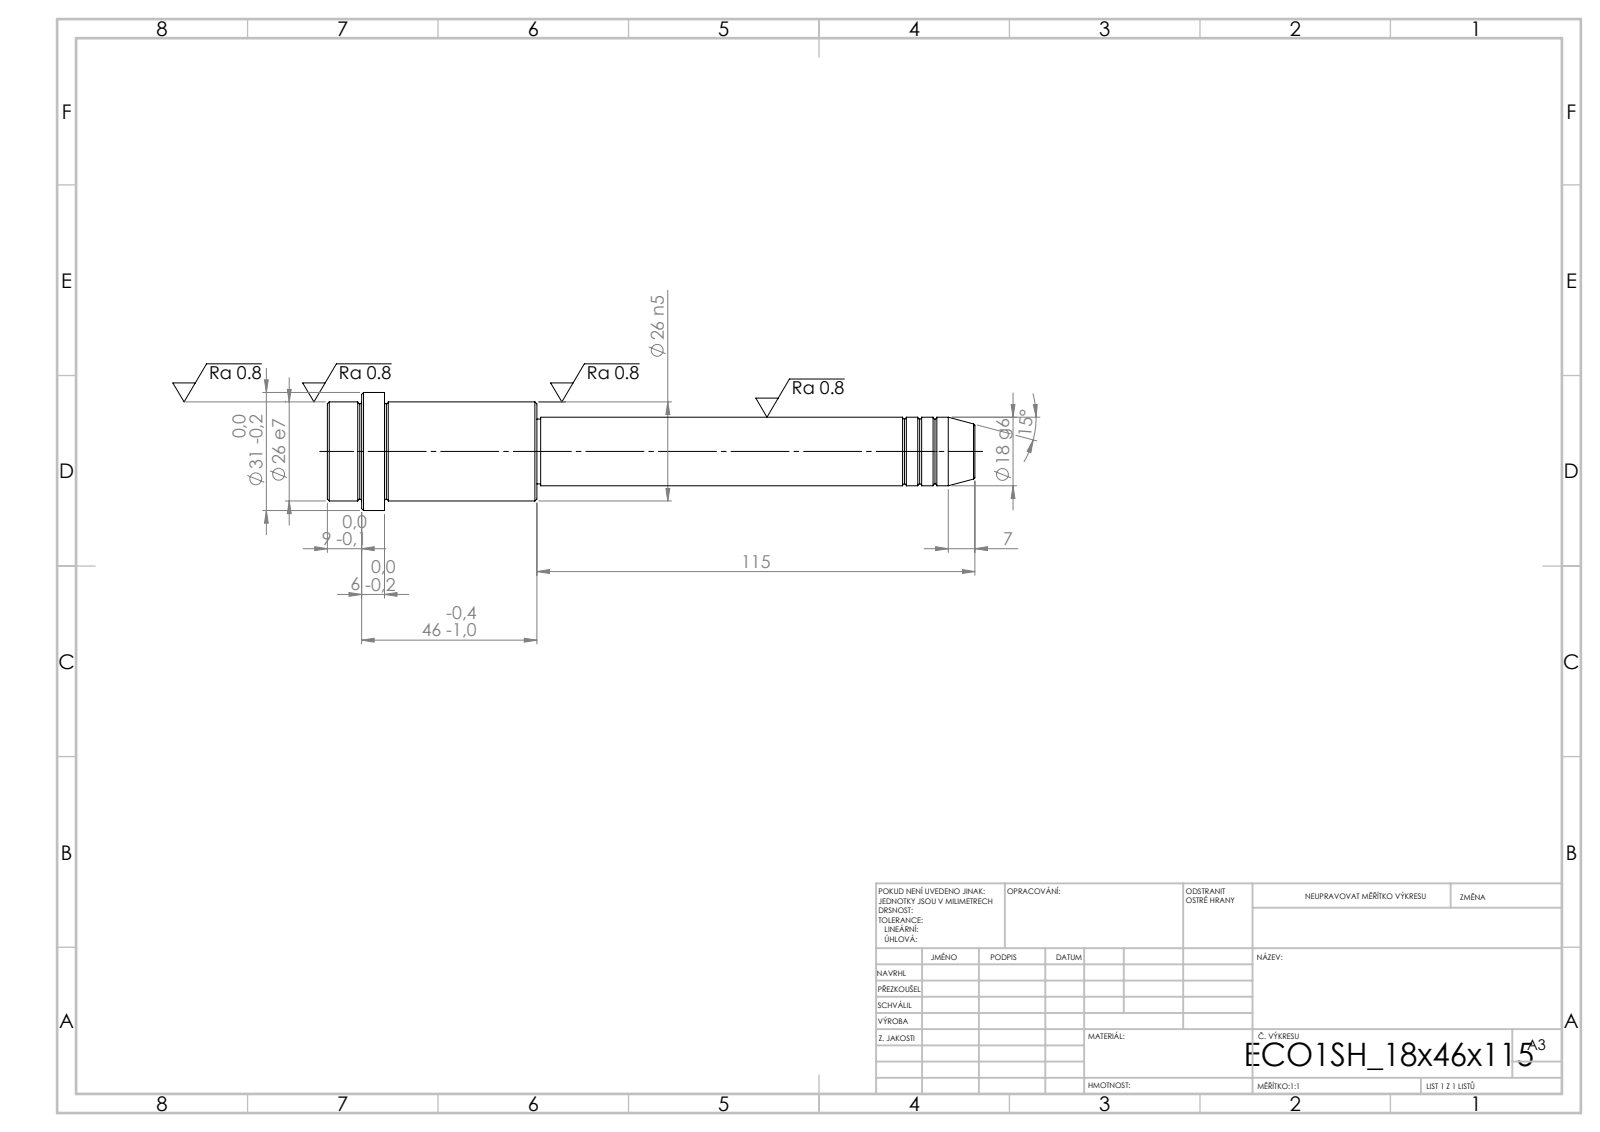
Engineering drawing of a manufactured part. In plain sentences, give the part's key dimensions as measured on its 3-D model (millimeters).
Its 3-D file was written by "SolidWorks 2019 (CONFIG_CONTROL_DESIGN)". It is 1 solid with 52 faces: 6 planar, 16 cylindrical and 30 other. Overall it measures 170 by 31 by 31 millimeters. Its volume is 59 274 cubic millimeters and its surface area 12 619 square millimeters. Round bosses or shafts: 1 of diameter 31, 1 of diameter 26, 1 of diameter 18, 1 of diameter 17. The main face-to-face distances are 55, 40, 15, 46, 6, 9, 115, 155, 161, 170.
